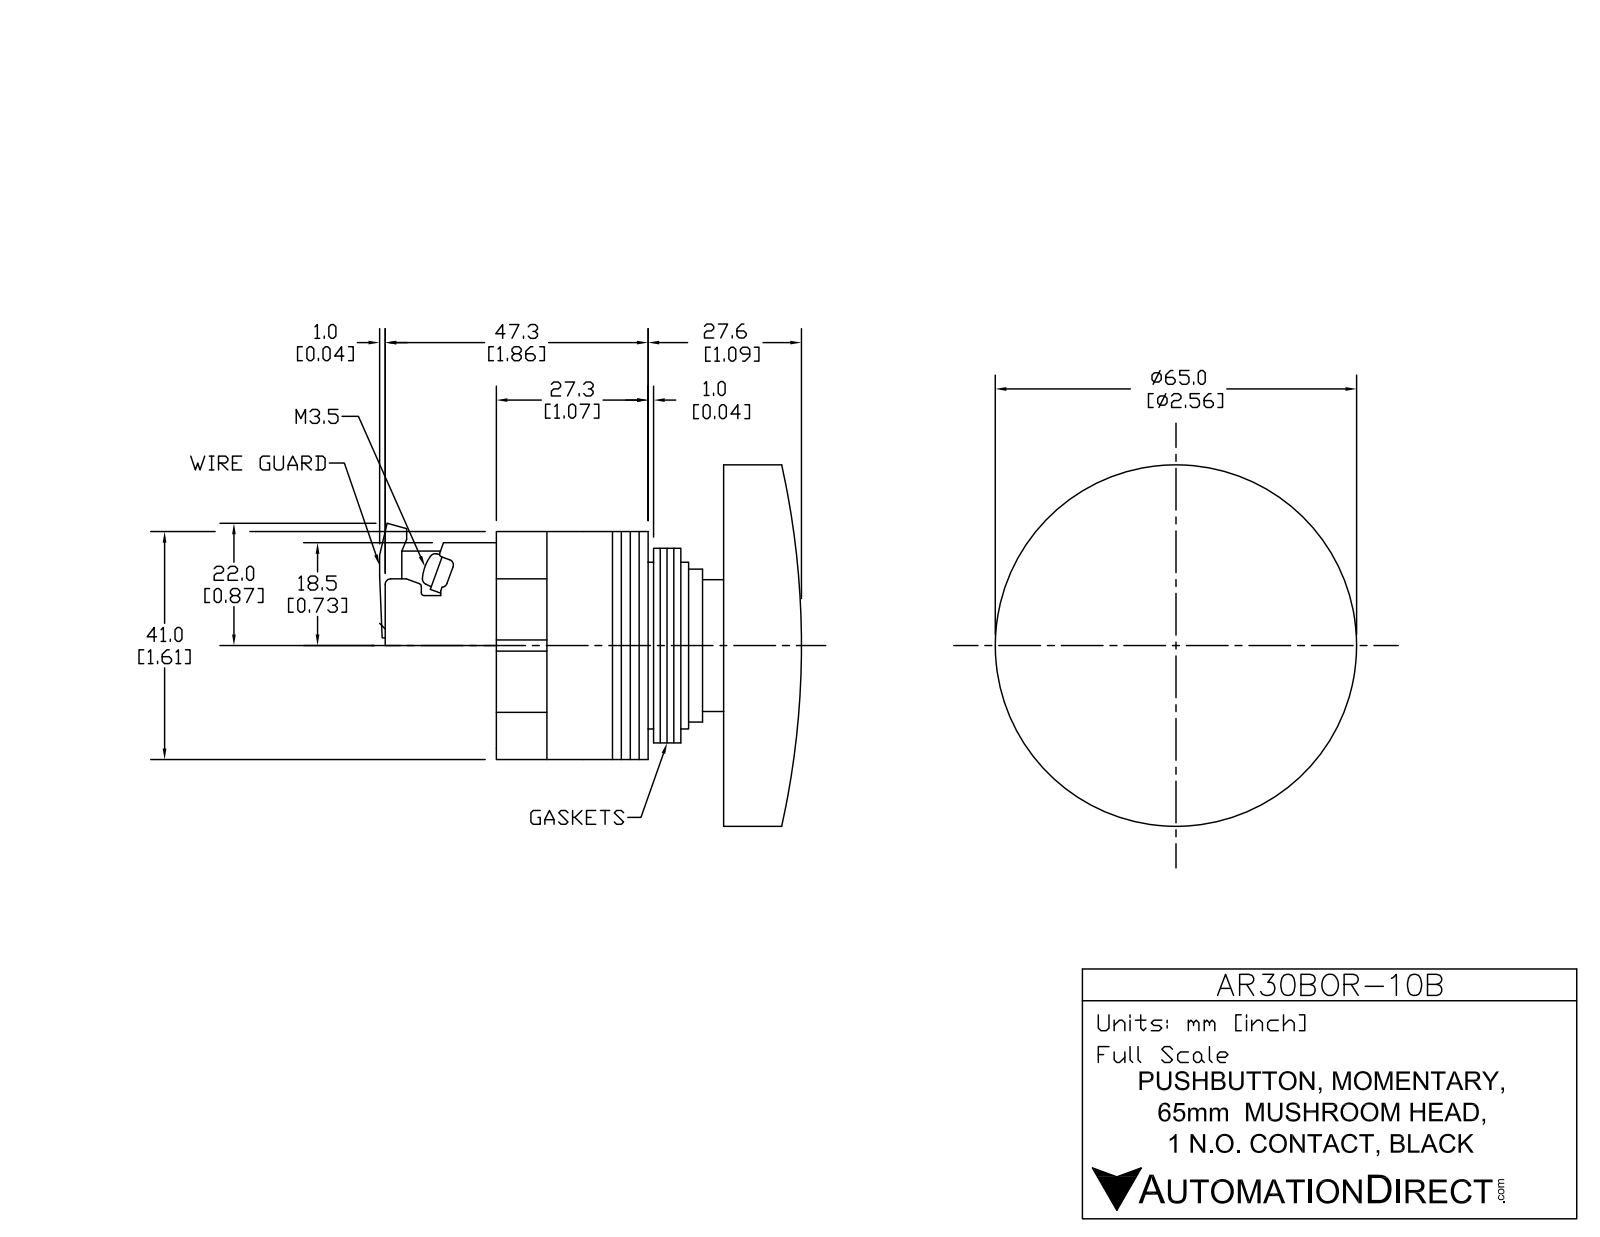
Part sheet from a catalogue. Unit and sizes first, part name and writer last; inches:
Units: inches
Overall size (bounding box): 2.992 × 2.559 × 2.559
Round holes (diameter × count): ⌀0.118 ×4, ⌀0.945 ×1, ⌀1.181 ×1, ⌀2.362 ×1
Round bosses / shafts (diameter × count): ⌀0.197 ×2, ⌀2.559 ×1, ⌀1.575 ×1, ⌀1.378 ×1, ⌀1.173 ×1
Partial cylindrical surfaces — rounded edges, fillets, slot ends (radius × count): R0.197 ×10, R0.02 ×8, R0.069 ×4, R0.118 ×4, R0.079 ×2
Main face-to-face distances: 0.063, 0.126, 0.63, 0.827, 0.197, 1.614, 0.189, 0.63, 0.197, 0.984
Hole centre spacings: 0.863, 1.22, 1.726
Volume: 4.519 in³ · Surface area: 58.25 in²
Bodies: 14 solids, 246 faces (140 planar, 92 cylindrical, 14 other)
Part name (STEP PRODUCT): AR30B0R-10B
STEP written by: SolidWorks 2017 (AUTOMOTIVE_DESIGN)
